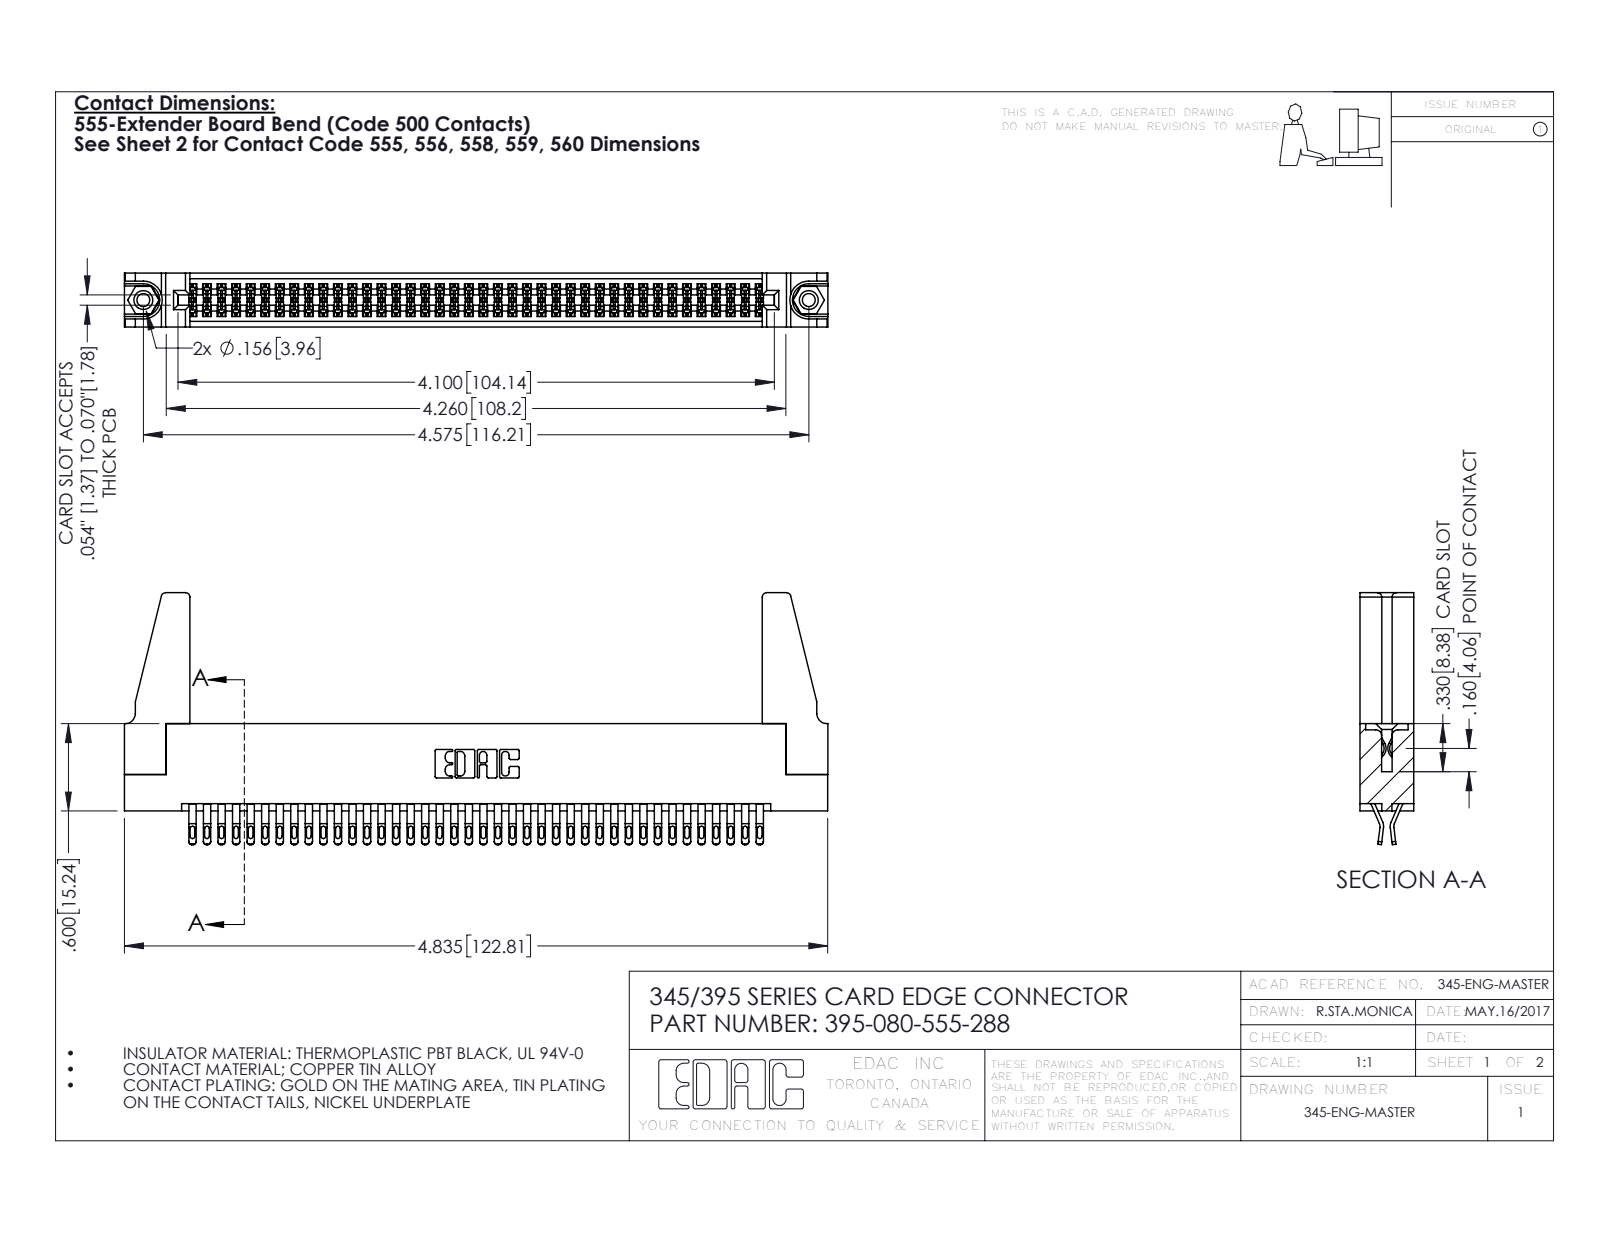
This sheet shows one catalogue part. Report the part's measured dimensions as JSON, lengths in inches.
{"part_name": "345-250-001_345-250-001-102; 395-080-555-288; 345-220-078_345-220-088; 345 Part_Flush Mounting Lugs - 0.156 Dia-TH (+1 more)", "step_written_by": "SolidWorks 2016 (CONFIG_CONTROL_DESIGN)", "units": "inches", "bodies": {"solids": 85, "faces": 4730, "planar": 2632, "cylindrical": 2082, "other": 16}, "overall_size": [4.836, 1.732, 0.37], "volume_in3": 0.94, "surface_area_in2": 33.86, "round_holes": [[0.089, 2], [0.125, 2], [0.156, 2], [0.064, 1]], "round_bosses_or_shafts": [[0.155, 2]], "partial_cylinders_radius": [[0.016, 200], [0.02, 160], [0.006, 120], [0.01, 22], [0.03, 8], [0.007, 6], [0.031, 6], [0.026, 3]], "face_to_face_distances": [0.072, 0.298, 0.37, 0.2, 0.025, 0.098, 0.272, 0.225, 0.175, 0.149], "hole_center_spacings": [0.27, 4.339, 4.575]}
